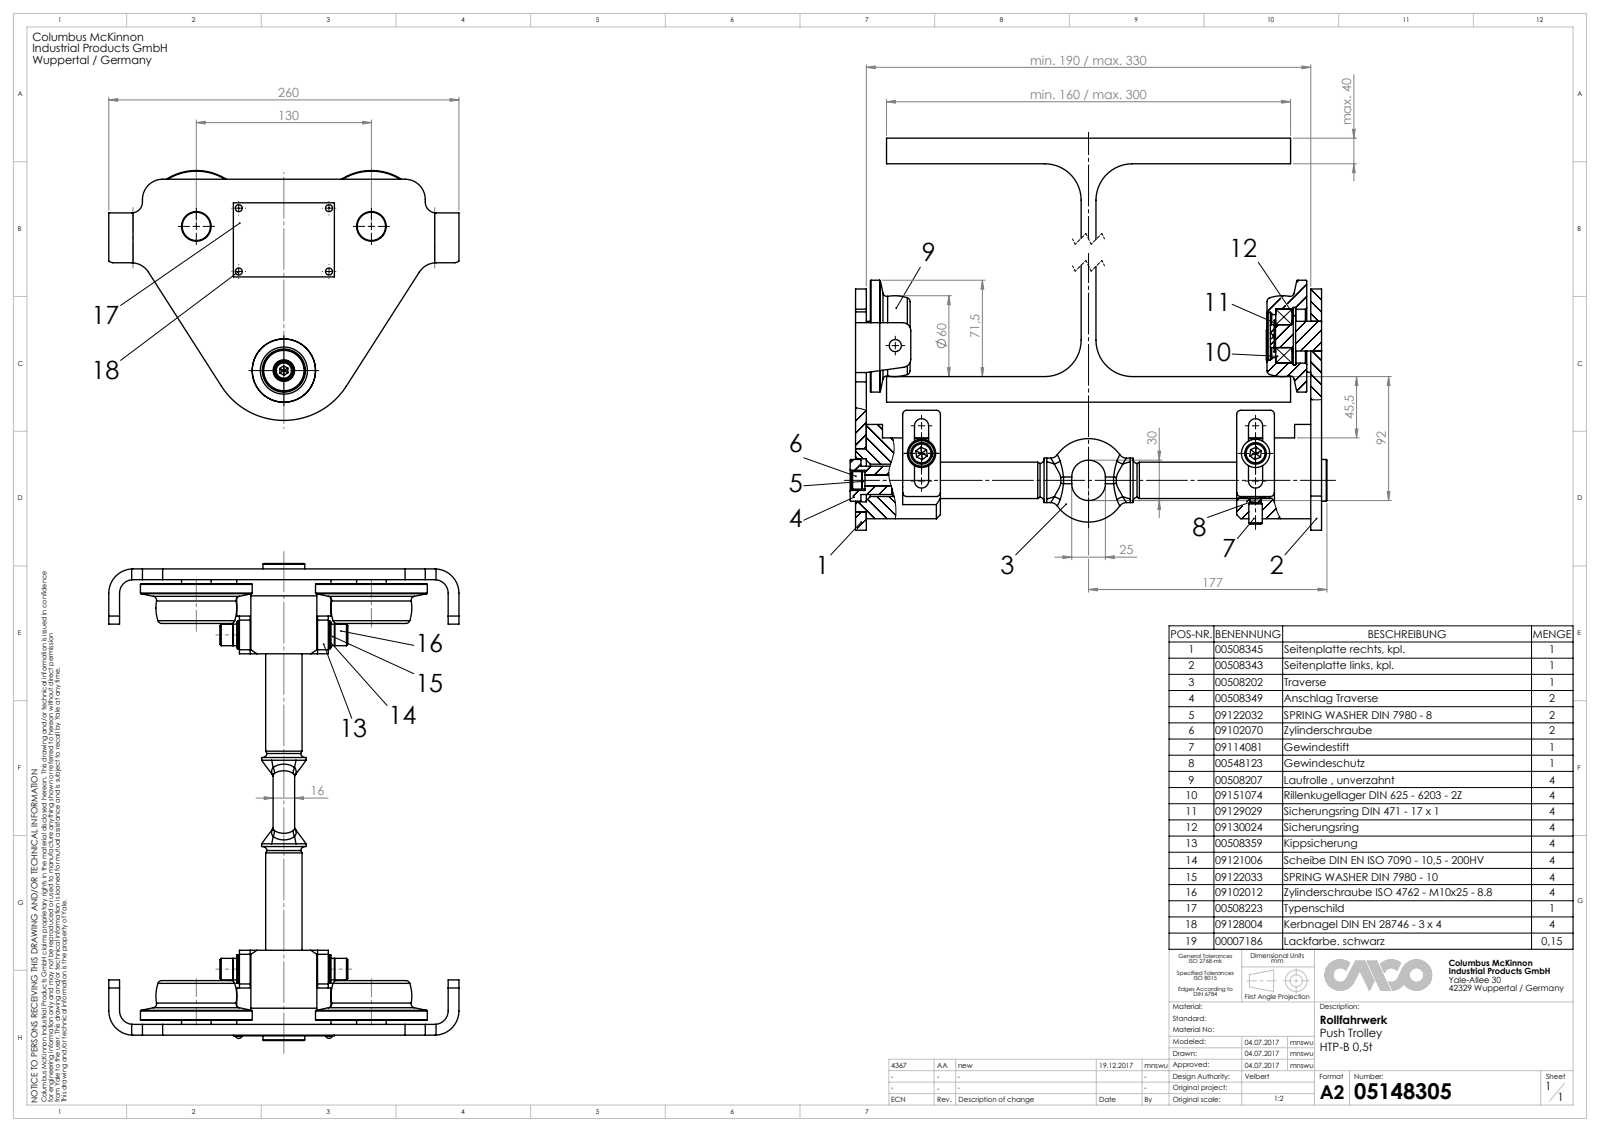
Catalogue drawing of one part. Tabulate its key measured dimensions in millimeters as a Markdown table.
| quantity | value |
| --- | --- |
| part name | HTP-B 0,5t |
| STEP written by | SolidWorks 2015 (AUTOMOTIVE_DESIGN) |
| units | millimeters |
| bodies | 55 solids, 1158 faces (398 planar, 442 cylindrical, 318 other) |
| overall size | 400 × 395 × 354 |
| volume | 7 380 000 mm³ |
| surface area | 1 105 000 mm² |
| round holes (diameter × count) | 2.5 × 7, 1.7 × 6, 3 × 4, 3.5 × 4, 8.5 × 3, 32 × 3, 2 × 2, 9 × 2, 10.2 × 2, 10.5 × 2, 16.2 × 2, 22 × 2 |
| round bosses / shafts (diameter × count) | 16 × 4, 5.2 × 4, 21 × 3, 10 × 3, 83 × 2, 42.5 × 2, 23.79 × 2, 17 × 2 |
| partial cylindrical surfaces (radius × count) | 3 × 8, 2.5 × 7, 1.7 × 6, 5.25 × 4, 6 × 4, 8 × 4, 10 × 4, 15 × 4 |
| main face-to-face distances | 19, 281, 300, 11, 262, 167.5, 8, 178.5, 159.5, 170.5 |
| hole center spacings | 8.38, 9.84, 18.35, 9.99, 130, 130.01, 4.25, 6.25 |
